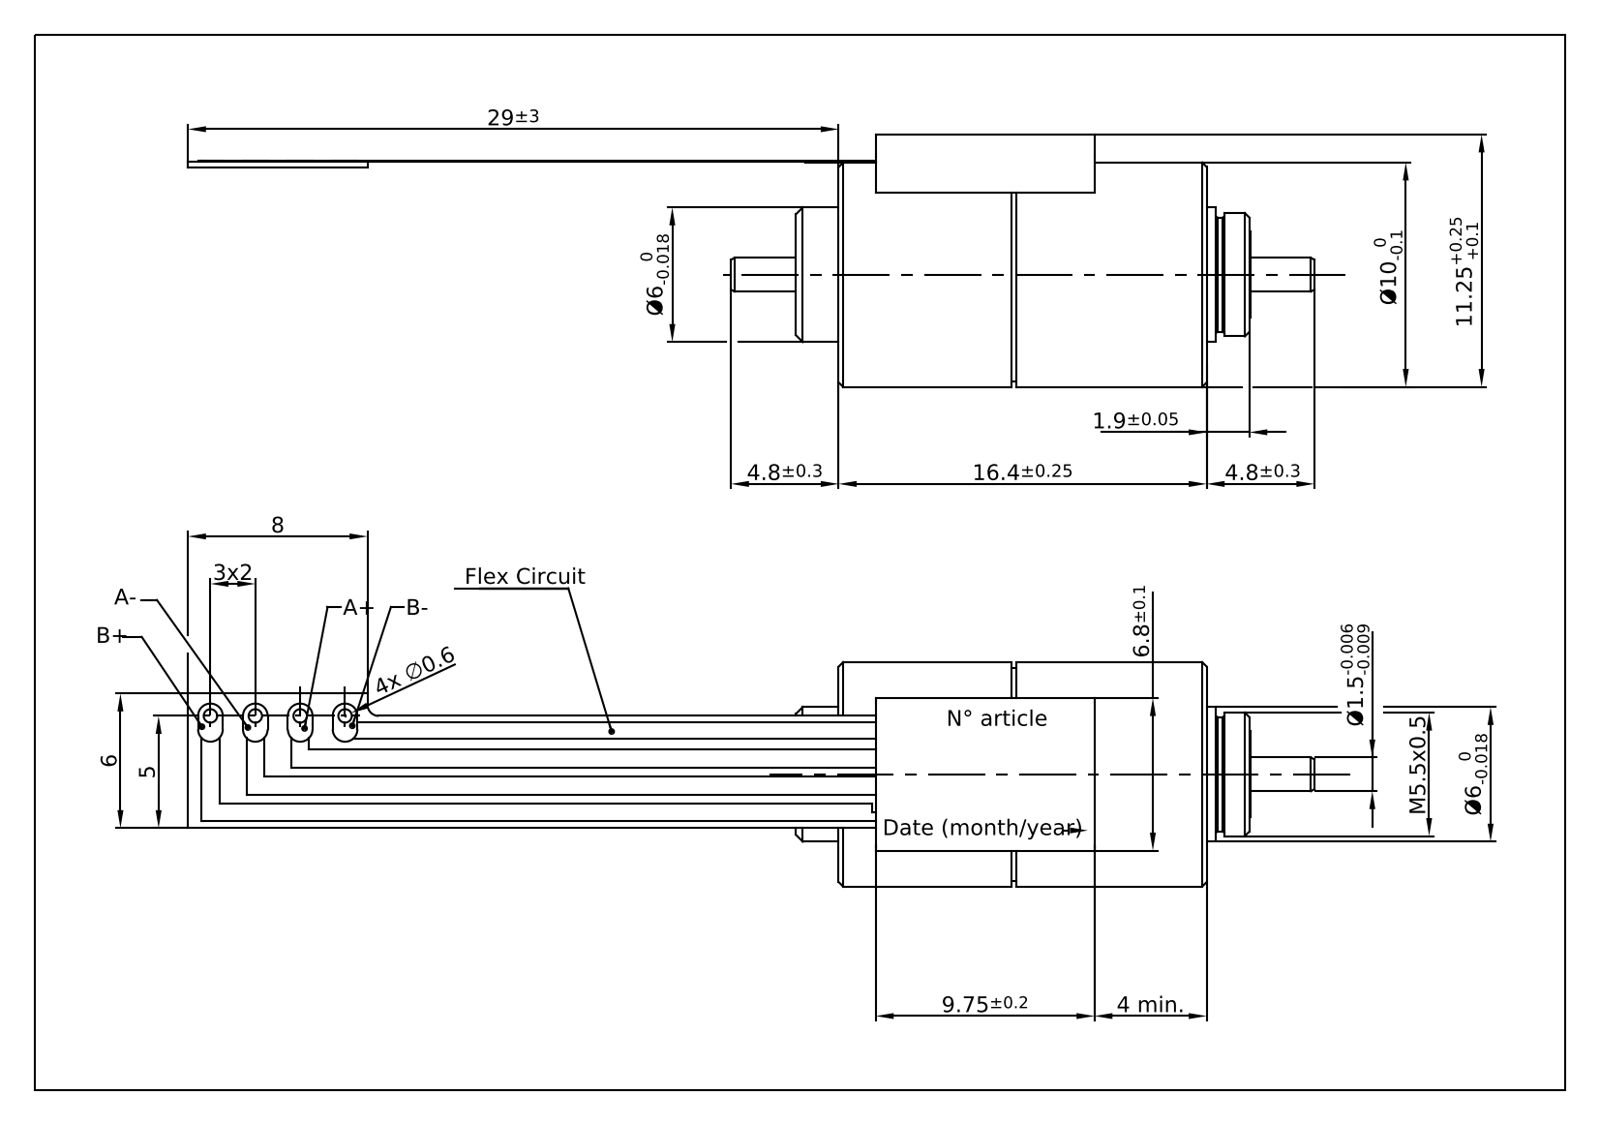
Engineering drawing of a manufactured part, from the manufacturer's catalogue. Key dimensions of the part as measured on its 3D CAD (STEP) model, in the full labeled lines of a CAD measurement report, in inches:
Part name (STEP PRODUCT): 2800010049_D_FAUT_1_1_1; 2281010004Z_D_FAUT_ASM_1_ASM_1__ASM; 2800010050_D_FAUT_1_1_1; 2271010004Z_D_FAUT_ASM_1_ASM_1__ASM (+8 more)
STEP written by: PRO/ENGINEER BY PARAMETRIC TECHNOLOGY CORPORATION, 2014310 (CONFIG_CONTROL_DESIGN)
Units: inches
Bodies: 6 solids, 142 faces (70 planar, 56 cylindrical, 16 other)
Overall size (bounding box): 1.976 × 0.443 × 0.394
Volume: 0.094 in³ · Surface area: 2.596 in²
Round holes (diameter × count): ⌀0.024 ×4, ⌀0.059 ×1, ⌀0.177 ×1, ⌀0.315 ×1
Round bosses / shafts (diameter × count): ⌀0.394 ×1, ⌀0.374 ×1, ⌀0.236 ×1, ⌀0.217 ×1, ⌀0.201 ×1, ⌀0.15 ×1
Partial cylindrical surfaces — rounded edges, fillets, slot ends (radius × count): R0.022 ×8, R0.008 ×6, R0.295 ×2, R0.02 ×1, R0.179 ×1, R0.201 ×1, R0.226 ×1, R0.246 ×1
Main face-to-face distances: 0.311, 0.343, 0.031, 0.335, 0.303, 0.378, 0.409, 0.295, 0.638, 0.067
Hole centre spacings: 0.079, 0.157, 0.236
